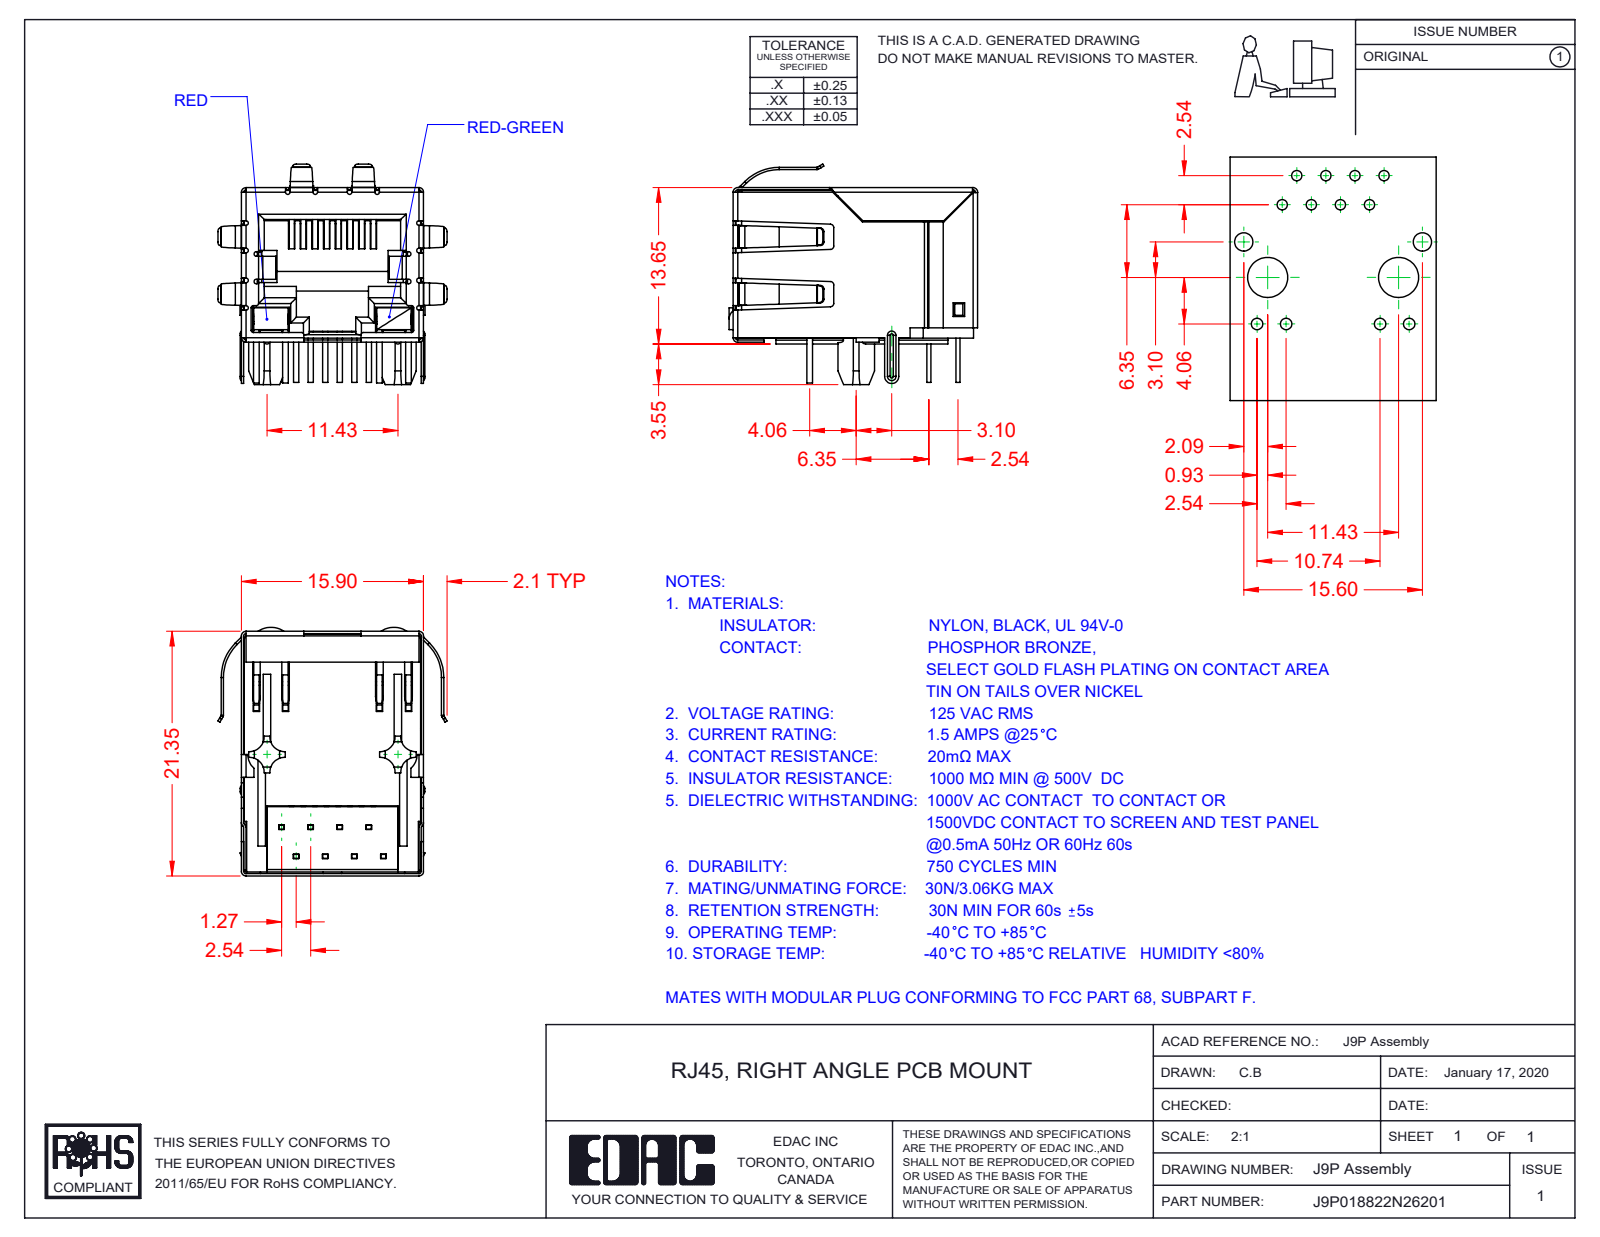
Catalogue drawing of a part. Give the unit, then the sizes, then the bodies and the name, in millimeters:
Units: millimetres
Overall size (bounding box): 21.7 × 20 × 19.25
Partial cylindrical surfaces — rounded edges, fillets, slot ends (radius × count): R0.2 ×39, R0.5 ×22, R0.3 ×20, R0.4 ×16, R1.3 ×8, R0.23 ×5, R0.11 ×4, R0.31 ×4
Main face-to-face distances: 15.45, 15.7, 15.65, 0.35, 0.54, 15.5, 12.36, 0.6, 1.4, 0.59
Volume: 2 687 mm³ · Surface area: 7 515 mm²
Bodies: 13 solids, 1474 faces (1042 planar, 338 cylindrical, 94 other)
Part name (STEP PRODUCT): 9P-LED Contacts; 9P-LED LED LH_2-Red; 9P-LED Shield; J9P018822N26202 (+4 more)
STEP written by: SolidWorks 2016 (CONFIG_CONTROL_DESIGN)
